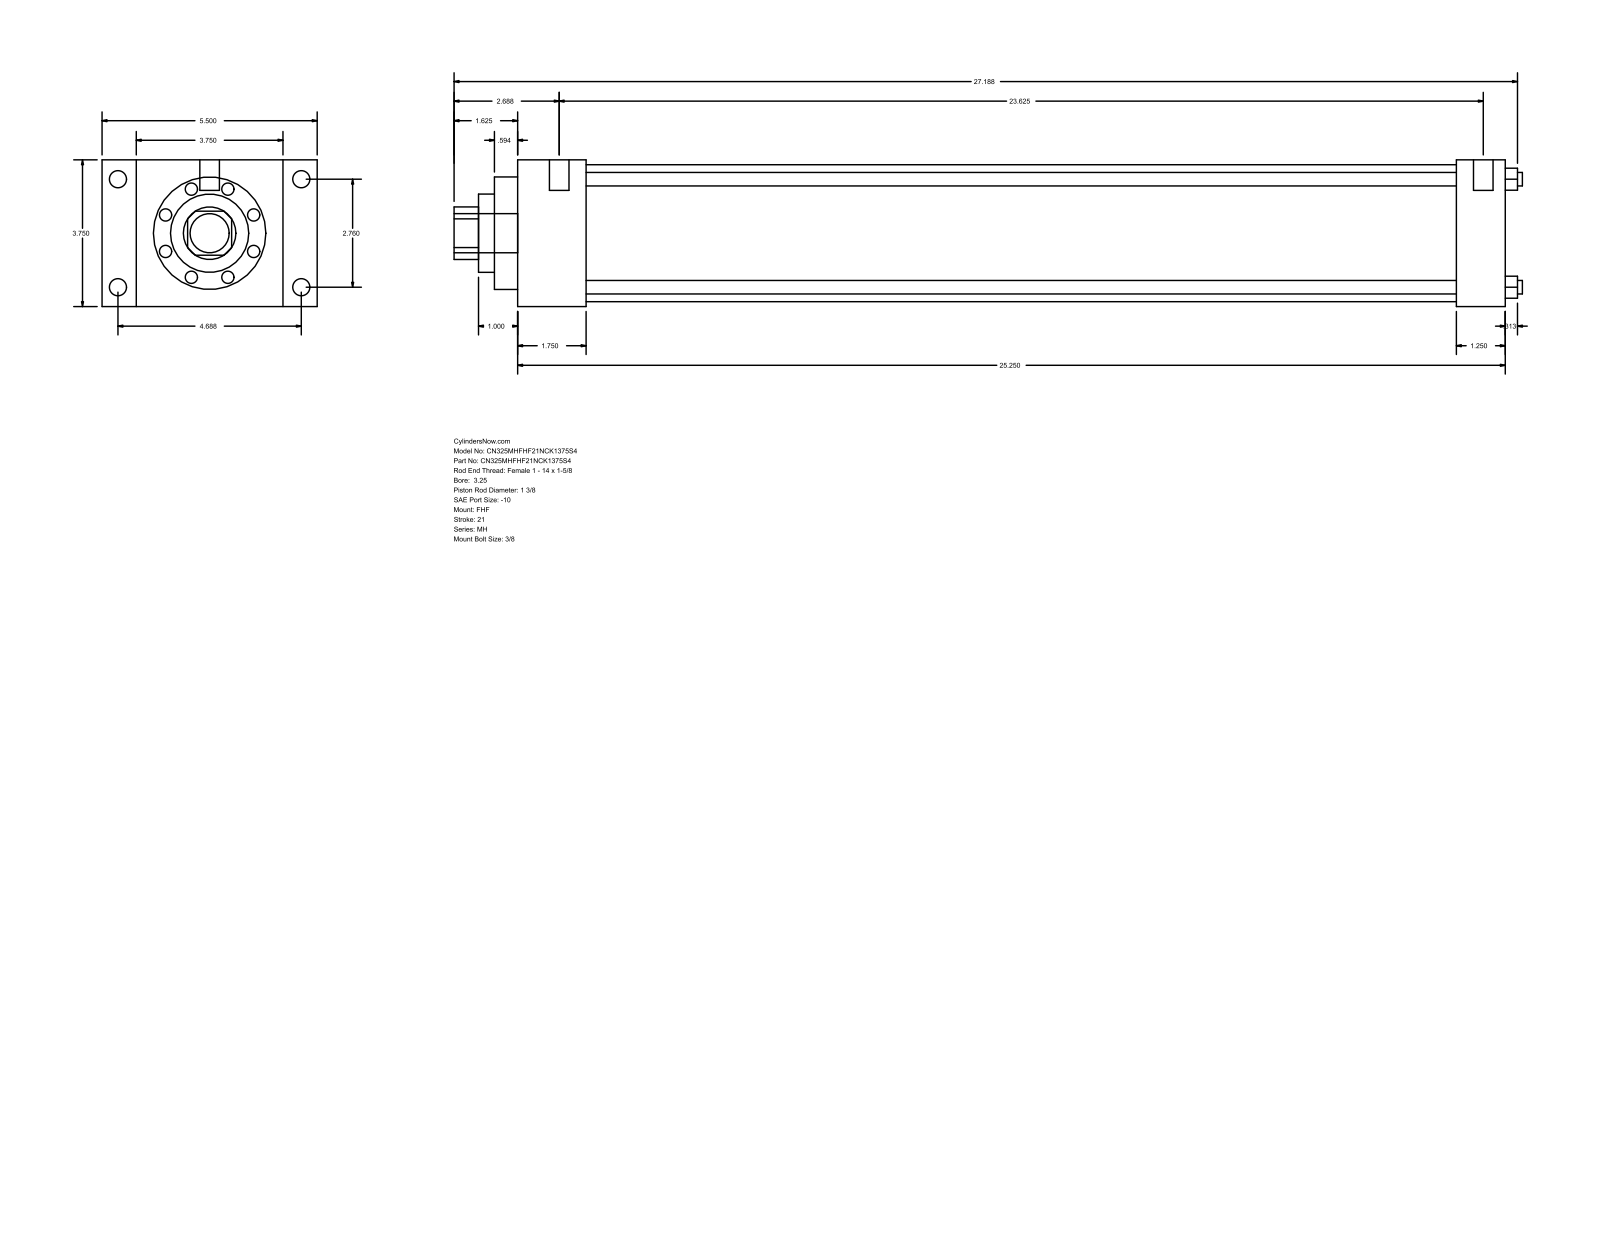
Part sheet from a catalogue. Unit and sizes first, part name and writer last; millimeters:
Units: millimetres
Overall size (bounding box): 693.74 × 139.7 × 95.25
Round holes (diameter × count): ⌀8.76 ×4, ⌀34.92 ×1, ⌀50.8 ×1, ⌀73.03 ×1, ⌀88.9 ×1
Round bosses / shafts (diameter × count): ⌀11.13 ×4, ⌀5.56 ×4, ⌀12.7 ×2, ⌀25.4 ×1
Partial cylindrical surfaces — rounded edges, fillets, slot ends (radius × count): R17.06 ×1
Main face-to-face distances: 95.24, 641.35, 44.45, 596.9, 22.23, 117.47, 139.7, 609.61, 565.16, 31.74
Hole centre spacings: 49.57, 70.1, 99.14
Bodies: 0 solids, 90 faces (61 planar, 29 cylindrical, 0 other)
Part name (STEP PRODUCT): MH_FHF__0325_1.375
STEP written by: GSSL Pune (CONFIG_CONTROL_DESIGN)
